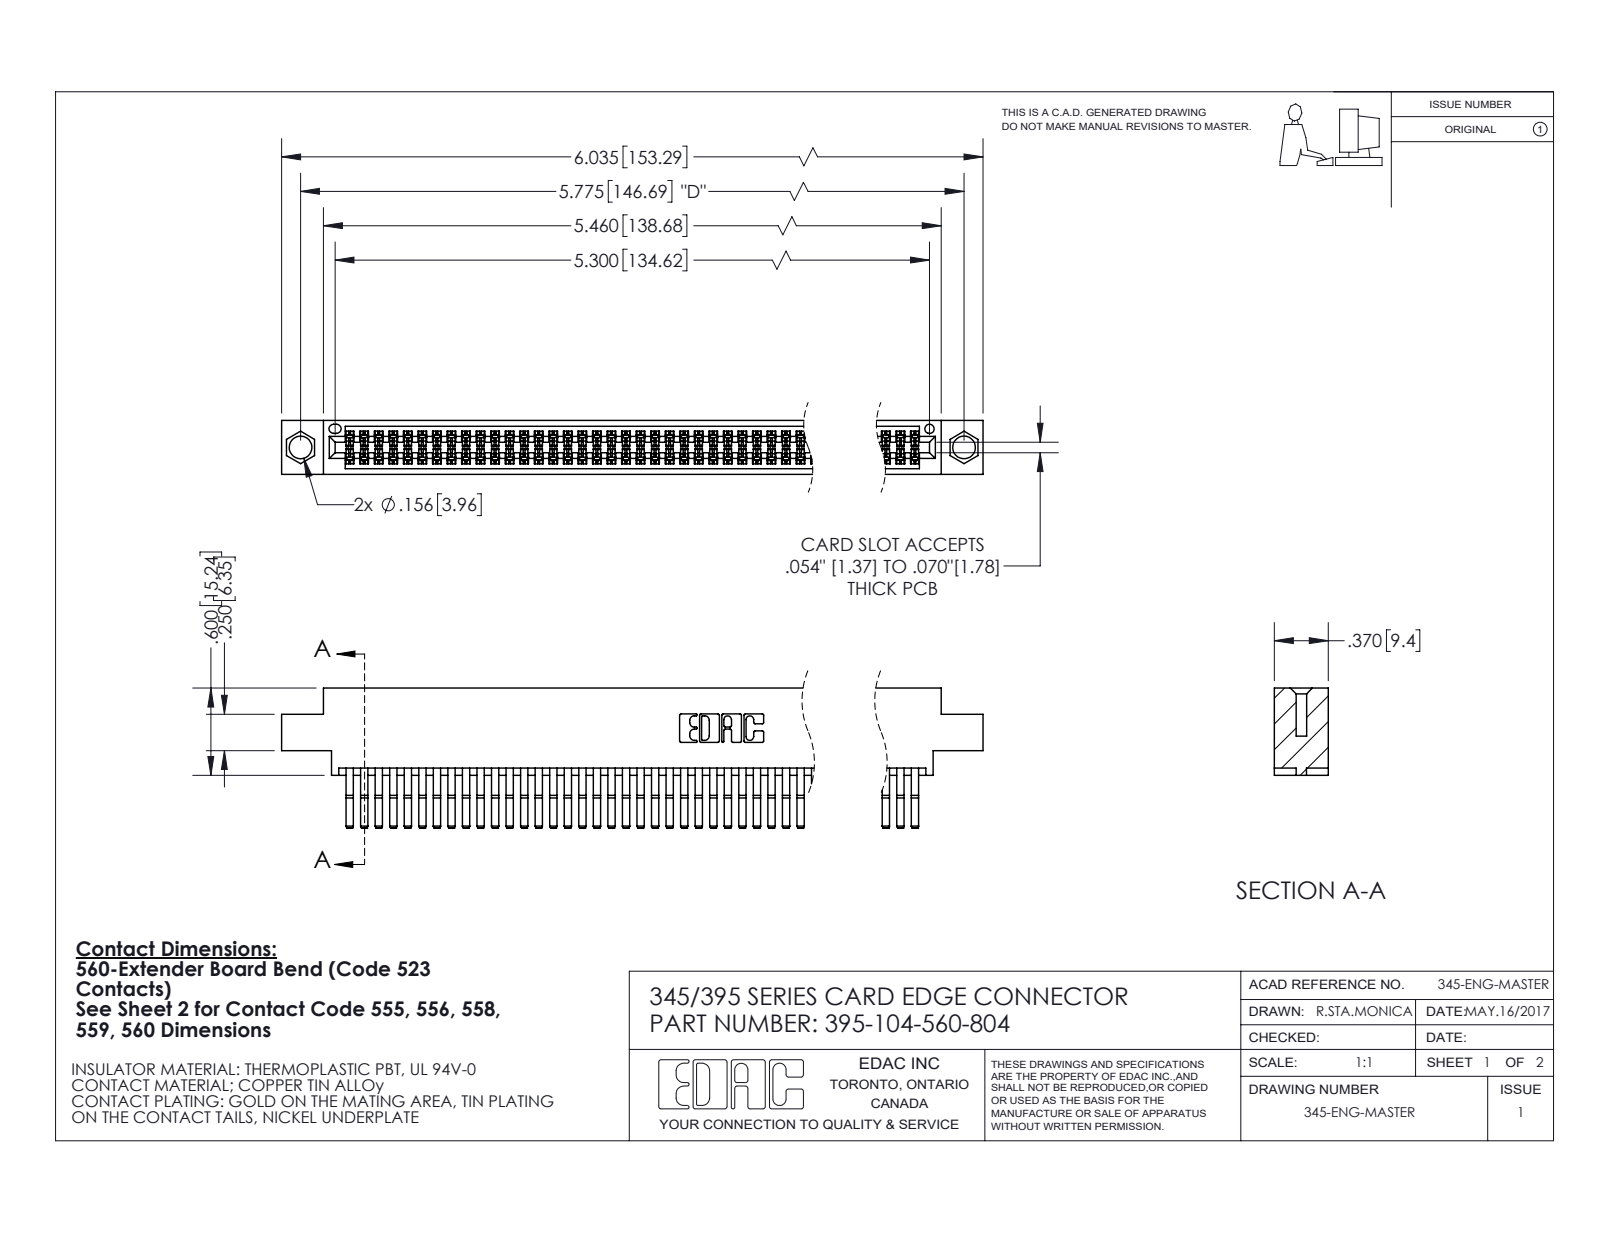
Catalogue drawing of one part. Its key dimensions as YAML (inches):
part_name: "345 Part_0.170 Offset - 0.156 Dia-TI; 395-104-560-804; 345-292-001_560 Tail"
step_written_by: "SolidWorks 2020 (CONFIG_CONTROL_DESIGN)"
units: inches
bodies: {solids: 105, faces: 5552, planar: 3530, cylindrical: 2022, other: 0}
overall_size: [6.035, 0.962, 0.37]
volume: 0.943
surface_area: 38.4
round_holes:
  - {diameter: 0.156, count: 2}
  - {diameter: 0.064, count: 1}
partial_cylinders:
  - {radius: 0.006, count: 208}
  - {radius: 0.01, count: 22}
  - {radius: 0.007, count: 6}
  - {radius: 0.031, count: 6}
  - {radius: 0.026, count: 3}
  - {radius: 0.01, count: 2}
  - {radius: 0.014, count: 2}
  - {radius: 0.019, count: 2}
face_to_face_distances: [0.025, 0.072, 0.298, 0.37, 0.2, 0.098, 0.272, 0.225, 0.175, 0.149]
hole_center_spacings: [0.27, 5.539, 5.775]
